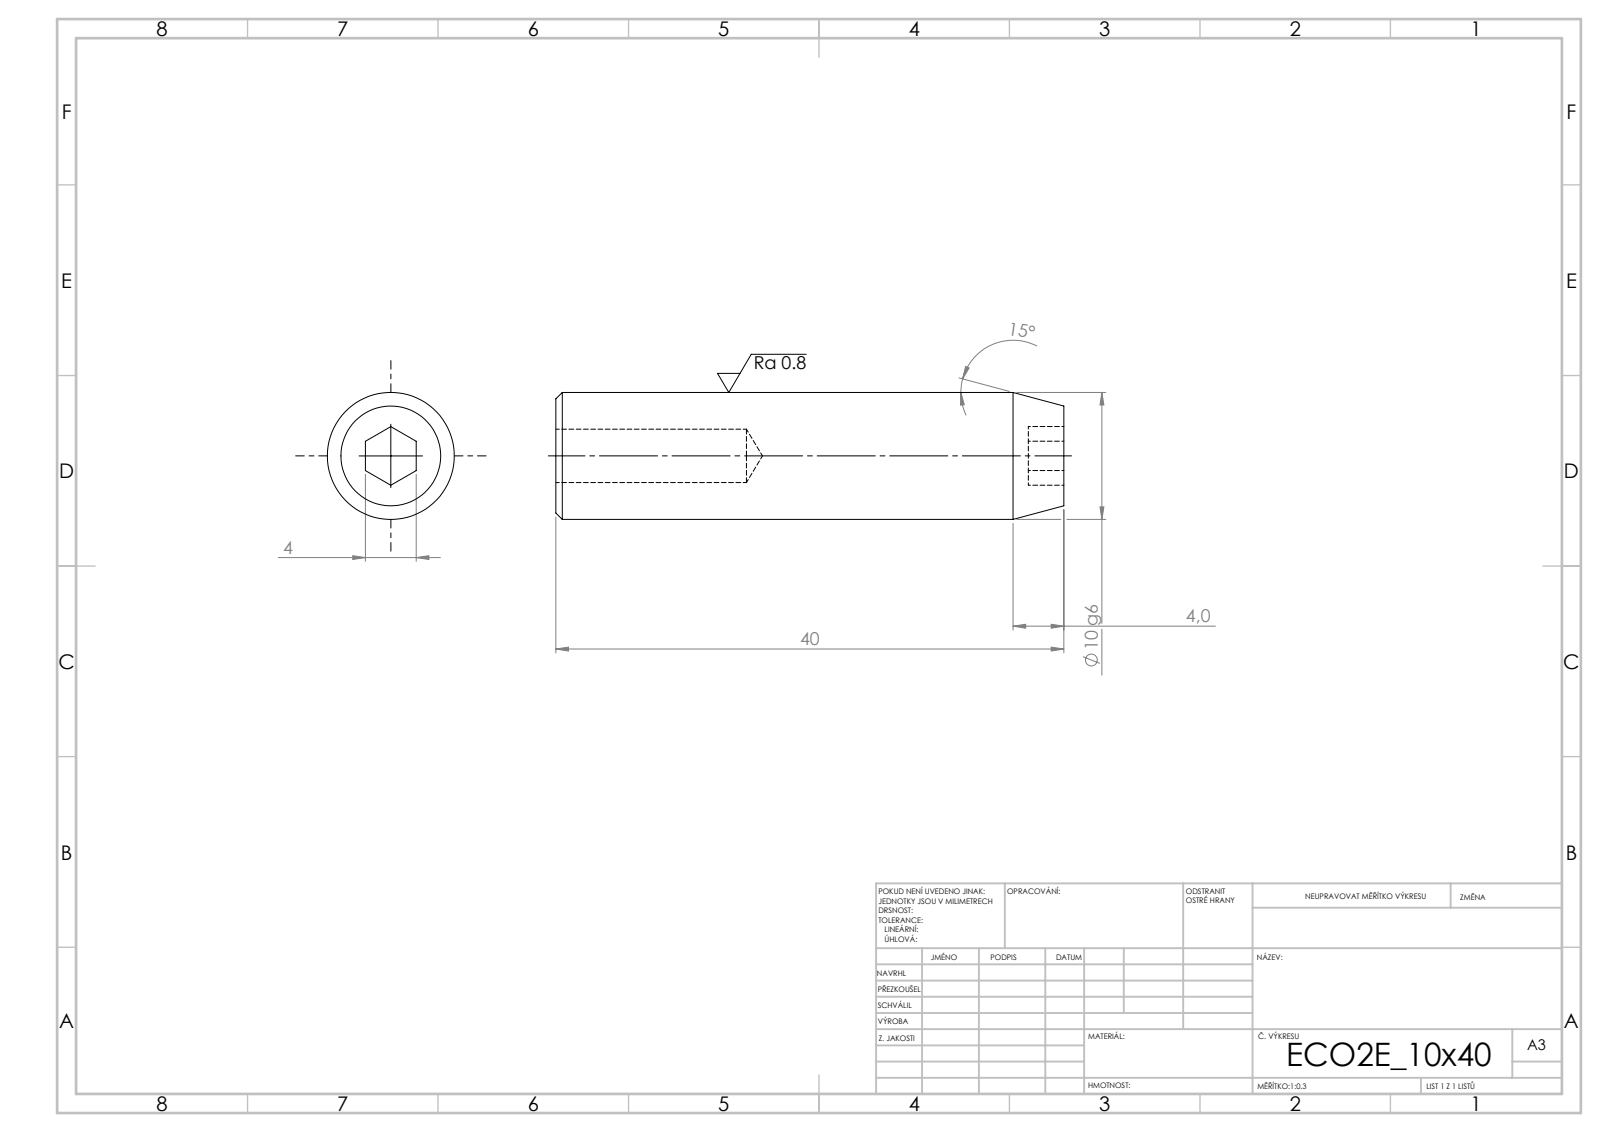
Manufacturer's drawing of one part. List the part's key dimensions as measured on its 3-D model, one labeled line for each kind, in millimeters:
STEP written by: SolidWorks 2019 (CONFIG_CONTROL_DESIGN)
Units: millimetres
Bodies: 1 solid, 19 faces (9 planar, 4 cylindrical, 6 other)
Overall size (bounding box): 40 × 10 × 10
Volume: 2 823 mm³ · Surface area: 1 604 mm²
Round holes (diameter × count): ⌀4.2 ×1
Round bosses / shafts (diameter × count): ⌀10 ×1
Main face-to-face distances: 40, 4, 2.8, 37.2
